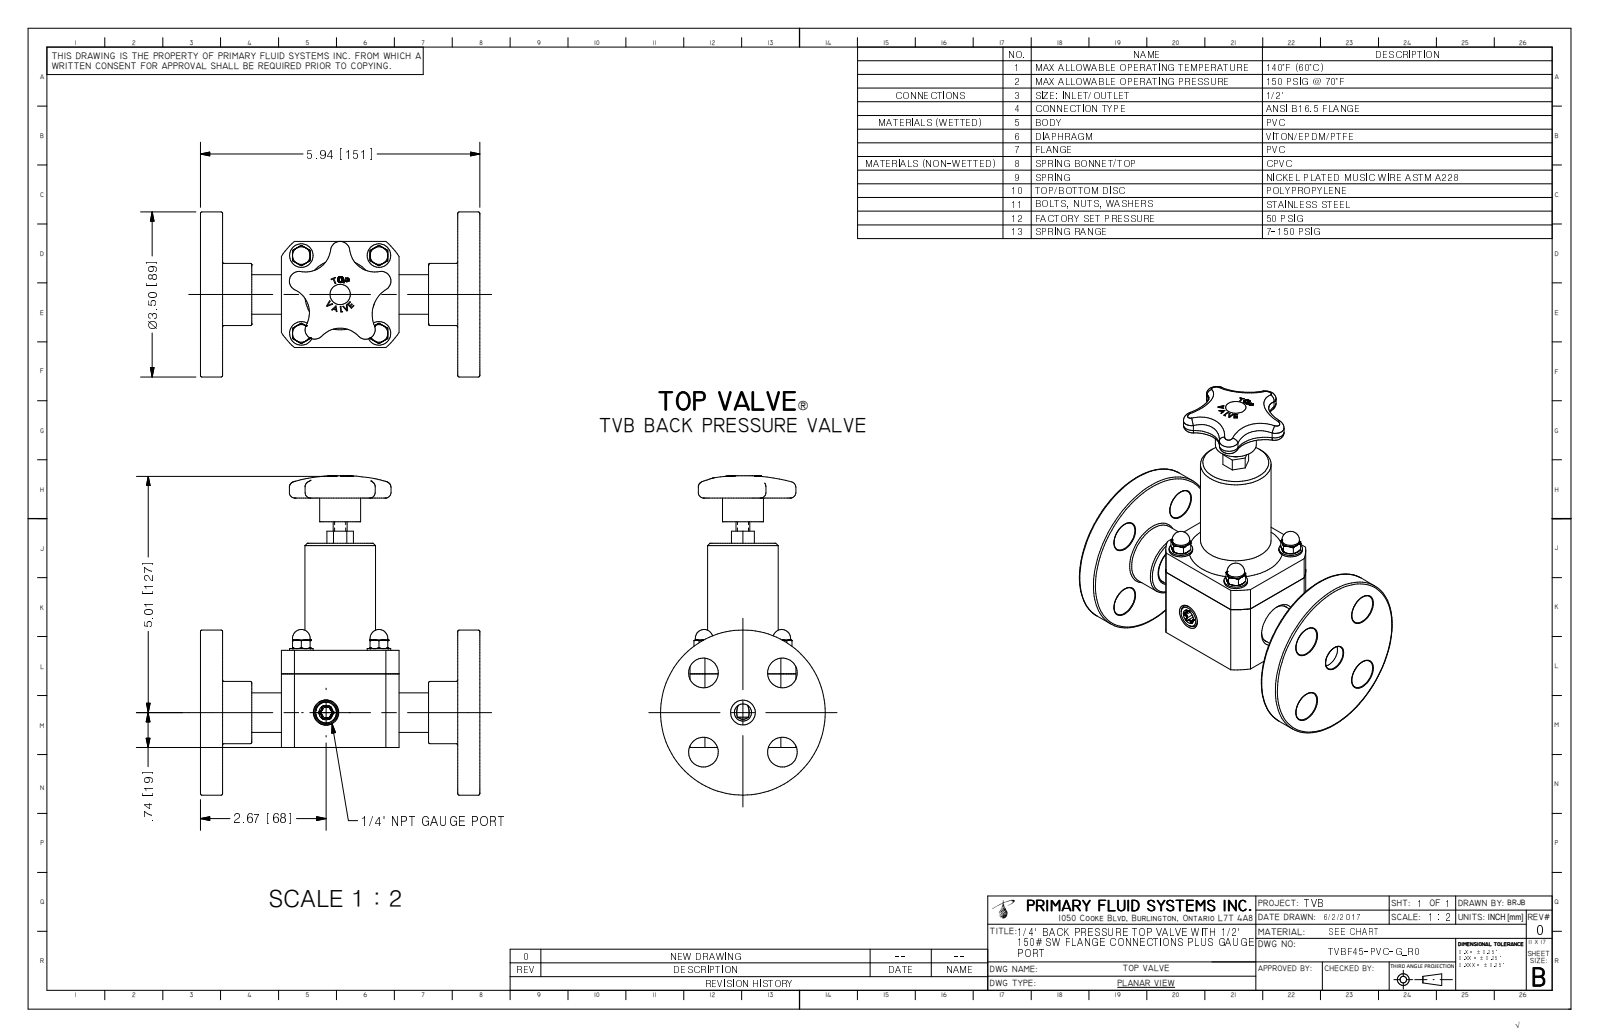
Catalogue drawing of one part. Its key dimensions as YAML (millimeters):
part_name: "TVBF45-PVC-G_R0"
step_written_by: "Autodesk Inventor 2009 (AUTOMOTIVE_DESIGN)"
units: millimeters
bodies: {solids: 1, faces: 415, planar: 156, cylindrical: 63, other: 196}
overall_size: [172, 150.9, 88.9]
volume: 423000
surface_area: 83160
round_holes:
  - {diameter: 3.7, count: 4}
  - {diameter: 16, count: 4}
  - {diameter: 13.4, count: 1}
round_bosses_or_shafts:
  - {diameter: 12.7, count: 4}
  - {diameter: 9.5, count: 4}
  - {diameter: 7.9, count: 4}
  - {diameter: 88.9, count: 1}
  - {diameter: 38.1, count: 1}
  - {diameter: 33.5, count: 1}
  - {diameter: 22.1, count: 1}
  - {diameter: 7.4, count: 1}
partial_cylinders:
  - {radius: 0.7, count: 6}
  - {radius: 2.2, count: 5}
  - {radius: 5.2, count: 5}
  - {radius: 13.6, count: 4}
  - {radius: 16.7, count: 4}
  - {radius: 15.9, count: 1}
  - {radius: 18.9, count: 1}
  - {radius: 37.8, count: 1}
face_to_face_distances: [11.9, 138.9, 150.9, 127, 107.2, 43.7, 31.8, 95.3, 57.2, 63.5]
hole_center_spacings: [41.9, 30.1, 30.2, 42.6, 42.7, 59.3, 60.3]
